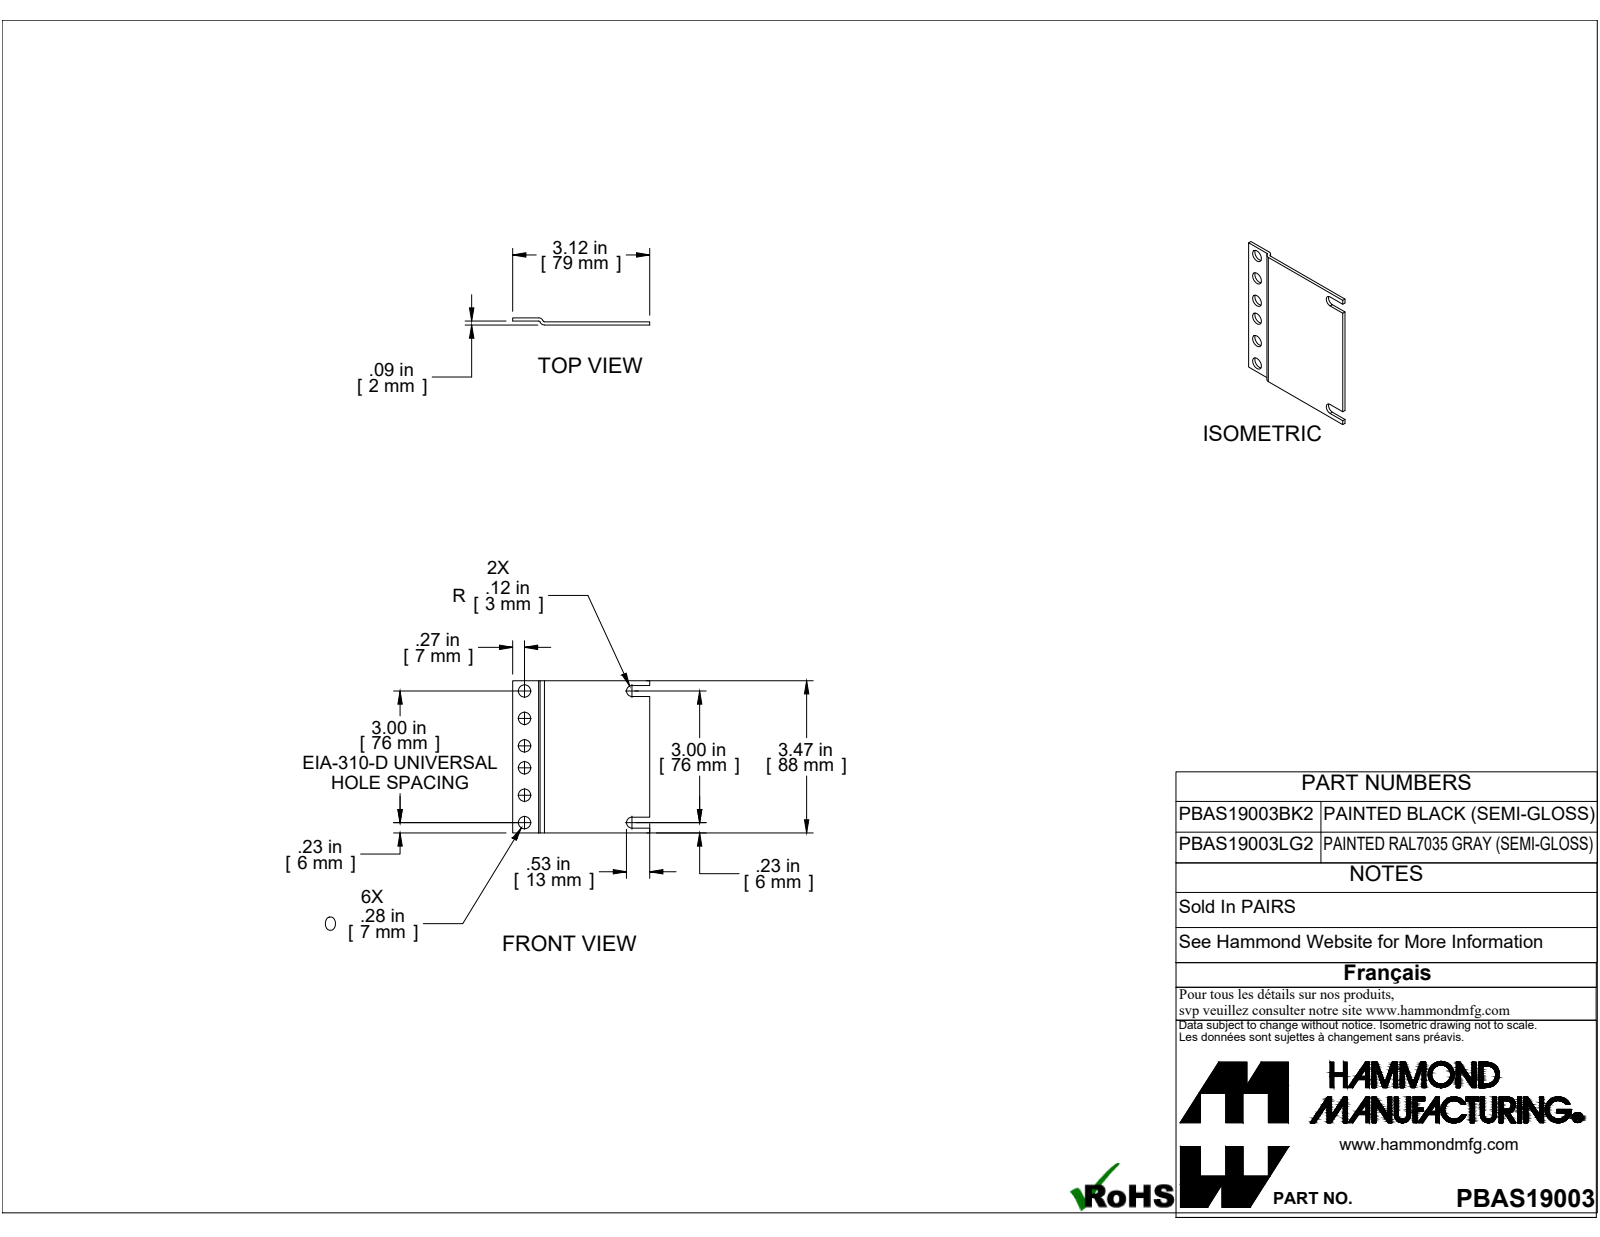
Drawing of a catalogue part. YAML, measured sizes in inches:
part_name: "PBAS19003LG2"
step_written_by: "SolidWorks 2019 (CONFIG_CONTROL_DESIGN)"
units: inches
bodies: {solids: 1, faces: 26, planar: 14, cylindrical: 12, other: 0}
overall_size: [3.468, 3.125, 0.162]
volume: 0.745
surface_area: 22.16
round_holes:
  - {diameter: 0.281, count: 6}
partial_cylinders:
  - {radius: 0.036, count: 2}
  - {radius: 0.108, count: 2}
  - {radius: 0.125, count: 2}
face_to_face_distances: [0.072, 0.09, 0.162, 0.018, 0.09, 0.072, 3.468, 3.125, 0.109, 3.359]
hole_center_spacings: [0.625, 0.625, 1.125, 1.25, 1.75, 2.375, 0.5, 1.75]
